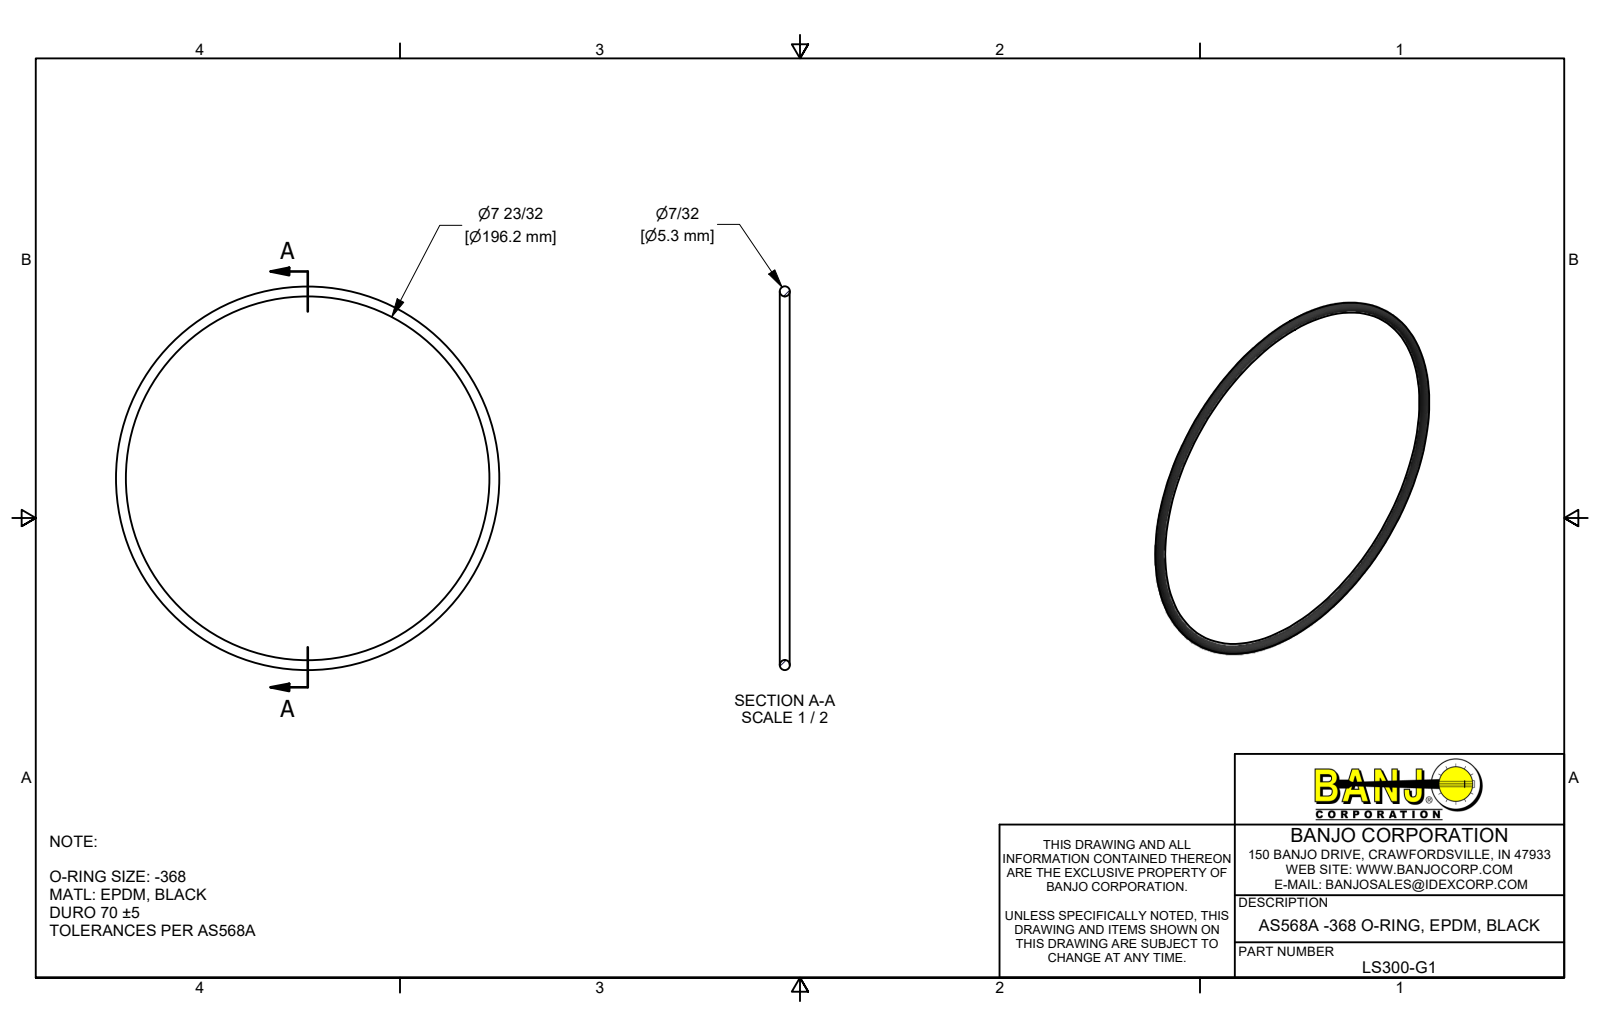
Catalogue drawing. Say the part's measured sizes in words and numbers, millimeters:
The part is named "LS300-G1". Its 3-D file was written by "Autodesk Inventor 2019 (AUTOMOTIVE_DESIGN)". It is 1 solid with 1 faces: 0 planar, 0 cylindrical and 1 other. Overall it measures 206.9 by 206.9 by 5.3 millimeters. Its volume is 14 100 cubic millimeters and its surface area 10 610 square millimeters.
